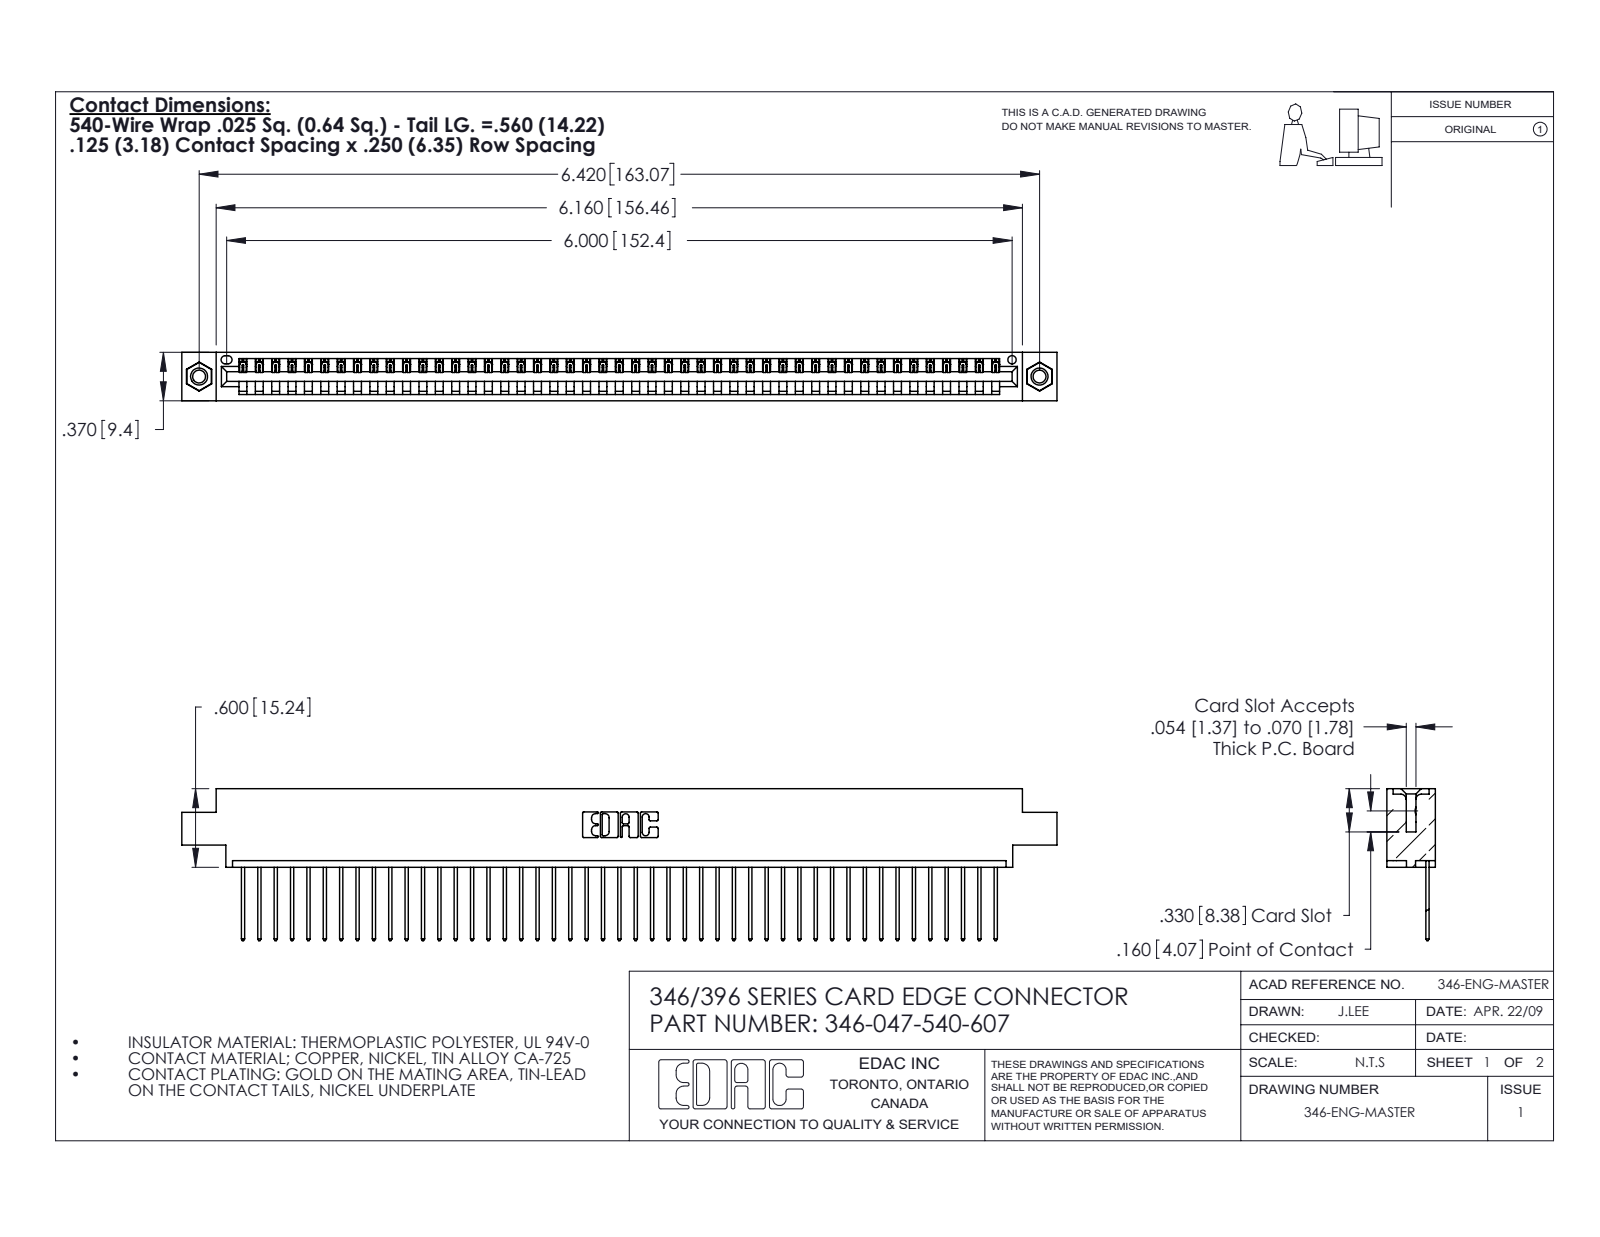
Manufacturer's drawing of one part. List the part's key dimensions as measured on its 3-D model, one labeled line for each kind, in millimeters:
Part name (STEP PRODUCT): 346-047-540-607; 346 Part_0.170 Offset - 0.156 Dia-TI; 345-250-001_345-250-005-103; 345-292-001_345-293-140
STEP written by: SolidWorks 2020 (CONFIG_CONTROL_DESIGN)
Units: millimetres
Bodies: 50 solids, 2912 faces (1992 planar, 904 cylindrical, 16 other)
Overall size (bounding box): 169.8 × 29.5 × 9.4
Volume: 16 200 mm³ · Surface area: 20 940 mm²
Round holes (diameter × count): ⌀2.5 ×2, ⌀3.2 ×2, ⌀4 ×2, ⌀1.6 ×1
Round bosses / shafts (diameter × count): ⌀3.9 ×2
Partial cylindrical surfaces — rounded edges, fillets, slot ends (radius × count): R0.2 ×94, R0.3 ×94, R0.3 ×22, R0.2 ×6, R0.8 ×6, R0.7 ×3, R0.8 ×2, R1 ×2
Main face-to-face distances: 1.2, 8.2, 9.4, 6.4, 1.8, 7.6, 0.6, 5.6, 3.8, 2.5
Hole centre spacings: 6.2, 157.8, 163.1
